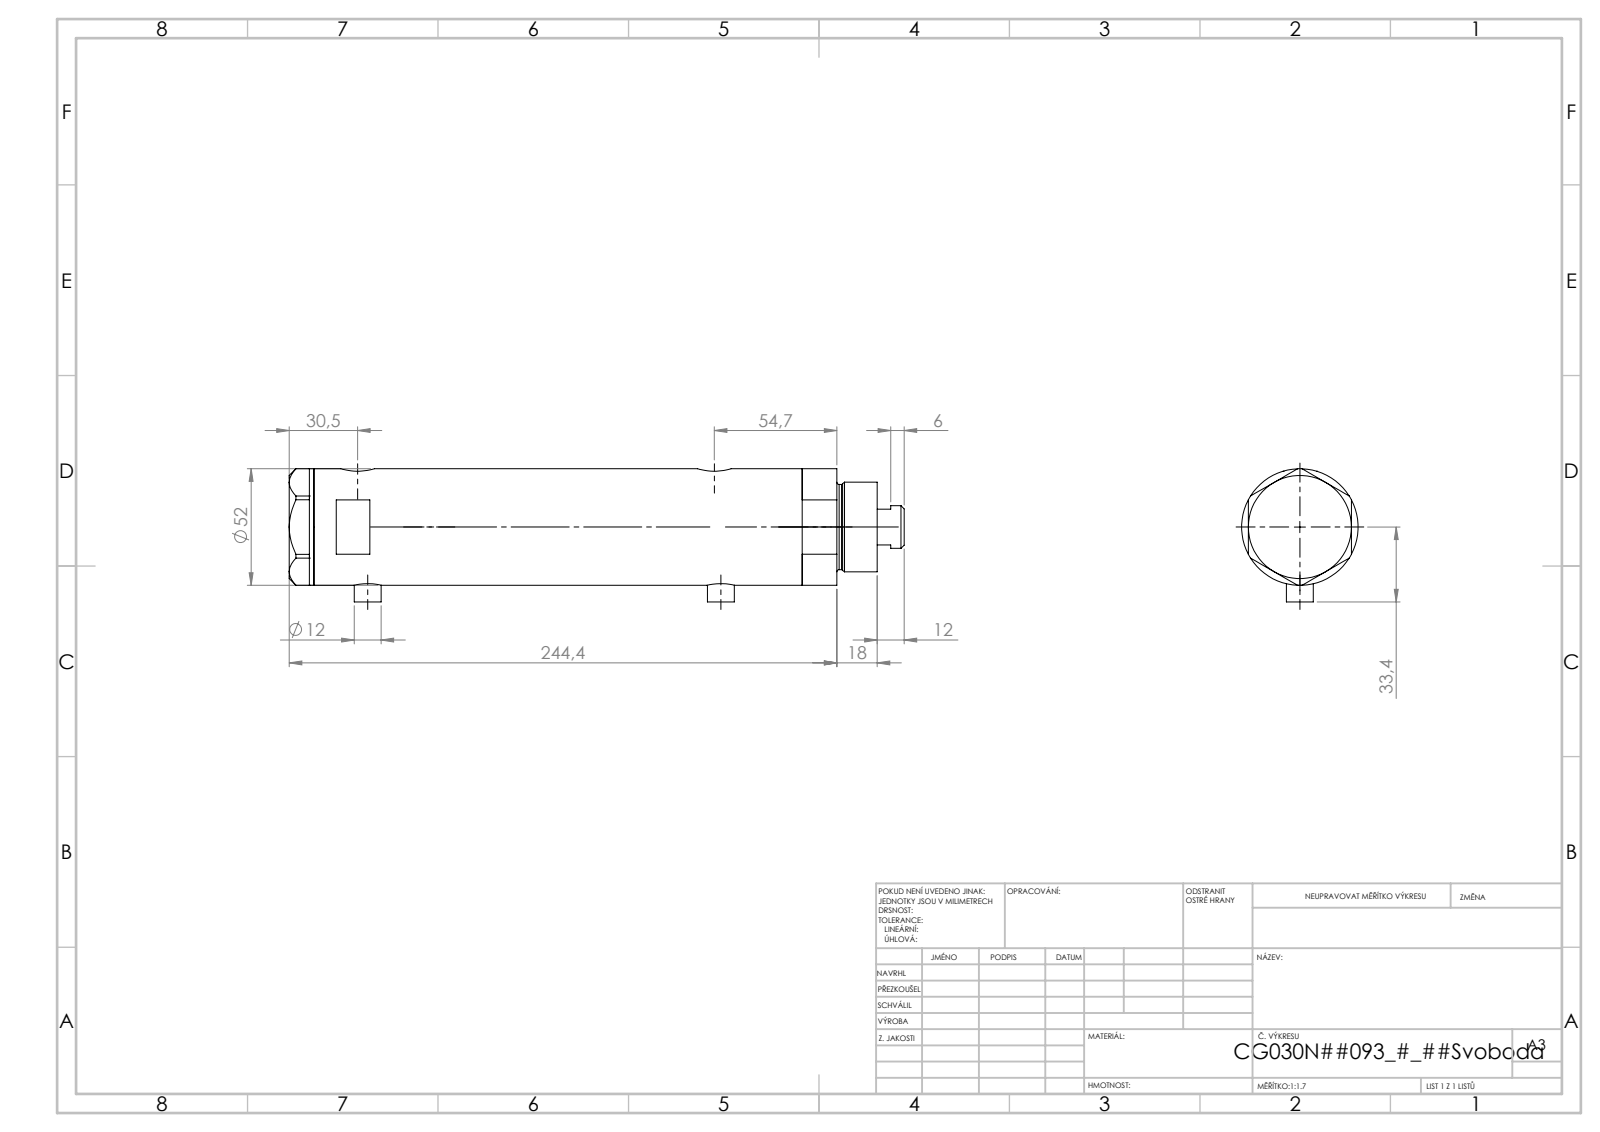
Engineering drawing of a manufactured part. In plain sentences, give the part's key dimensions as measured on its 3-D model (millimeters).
The part is named "V270CG_MIDDLE; V270CG_VC; V270CG_BACK; V270CG_FRONT". Its 3-D file was written by "SolidWorks 2019 (CONFIG_CONTROL_DESIGN)". It is 4 solids with 140 faces: 67 planar, 53 cylindrical and 20 other. Overall it measures 274.4 by 59.4 by 52 millimeters. Its volume is 500 675 cubic millimeters and its surface area 107 215 square millimeters. Round holes: 2 of diameter 5, 2 of diameter 9.73, 2 of diameter 12.5, 2 of diameter 15, 1 of diameter 6.5, 1 of diameter 20, 1 of diameter 21.5, 1 of diameter 30, 1 of diameter 33, 1 of diameter 44. Round bosses or shafts: 2 of diameter 12, 1 of diameter 52, 1 of diameter 40, 1 of diameter 38, 1 of diameter 19. The main face-to-face distances are 181.5, 23.8, 157.7, 11, 34.8, 192.5, 46, 228.9, 217.9, 194.1. The hole center spacings are 2.9, 4.5, 154.7, 157.6, 159.2, 162.1.
